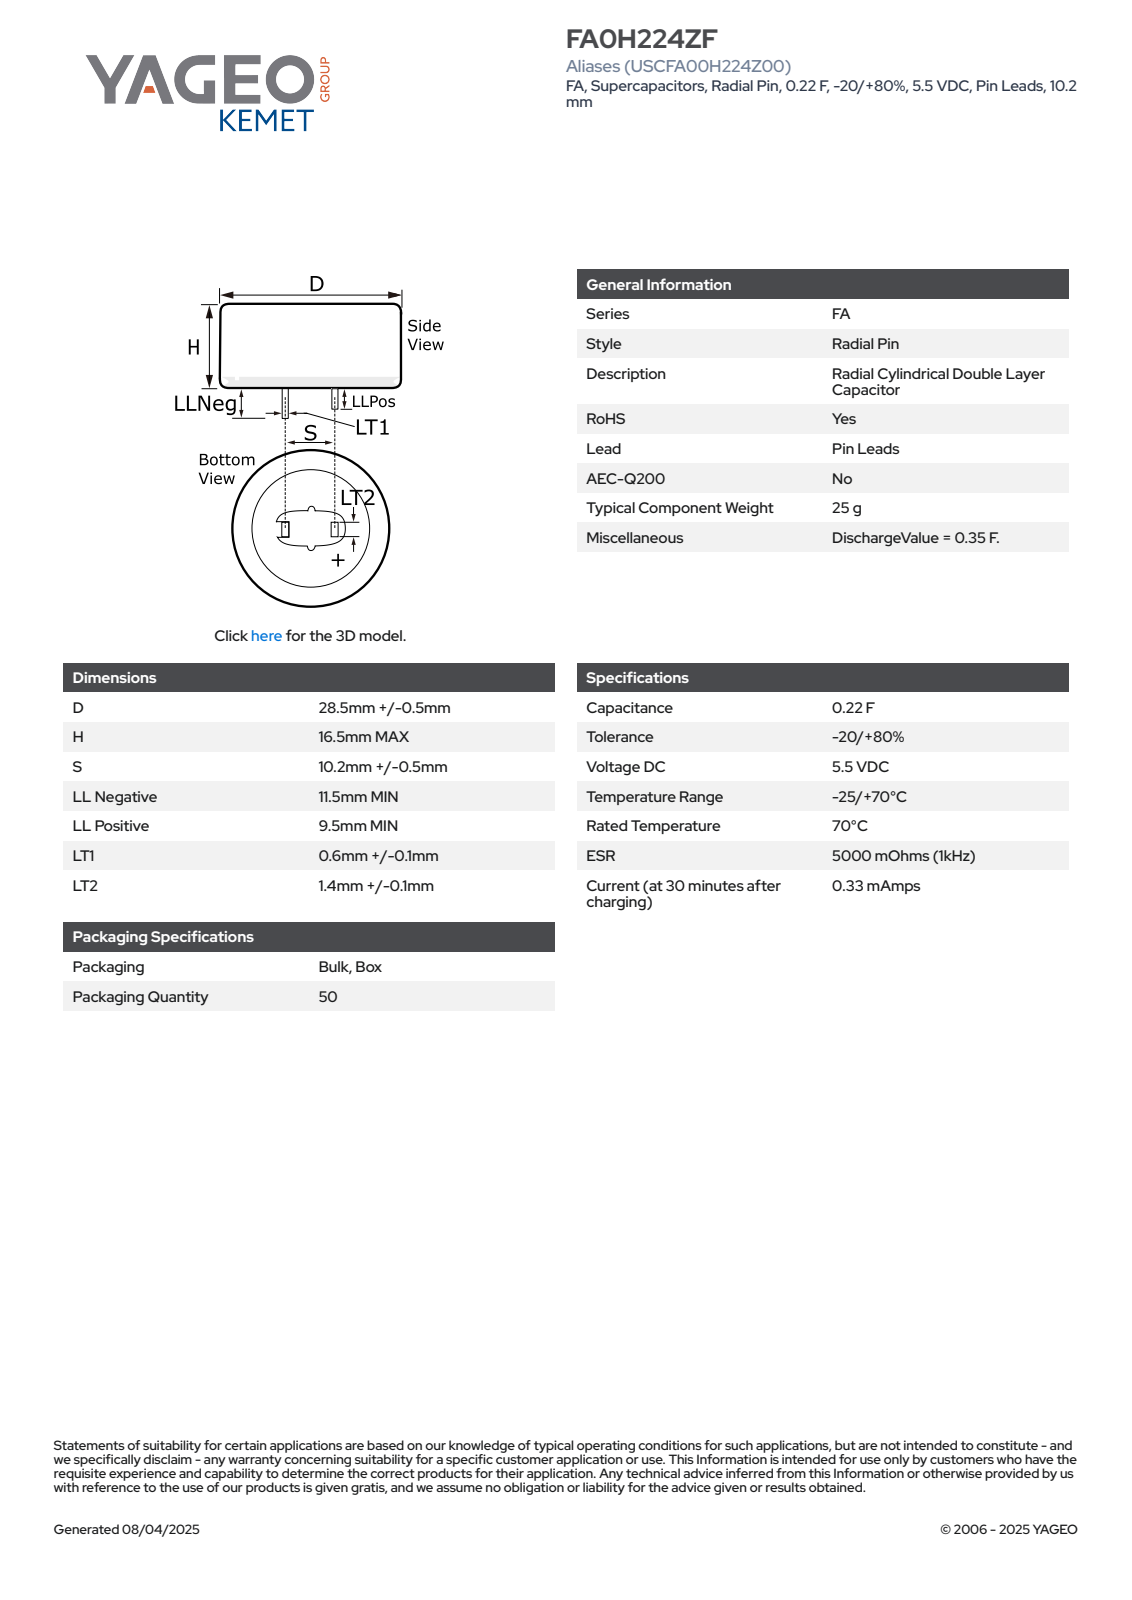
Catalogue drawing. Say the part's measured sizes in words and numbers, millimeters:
The part is named "CDR_LPLLN_D29L16.5S10.2LLNEG11.5LLPOS9.5LT10.7LT21.5". Its 3-D file was written by "SolidWorks 2014 (AUTOMOTIVE_DESIGN)". It is 1 solid with 78 faces: 70 planar, 4 cylindrical and 4 other. Overall it measures 29 by 29 by 28 millimeters. Its volume is 10 877 cubic millimeters and its surface area 2 833 square millimeters. Round bosses or shafts: 1 of diameter 29. Partial cylindrical surfaces (rounded edges, fillets, slot ends): 1 of radius 14.51. The main face-to-face distances are 16.5, 0.7, 10.2, 9.5, 1.5, 10.9, 11.5, 28, 2, 26.
